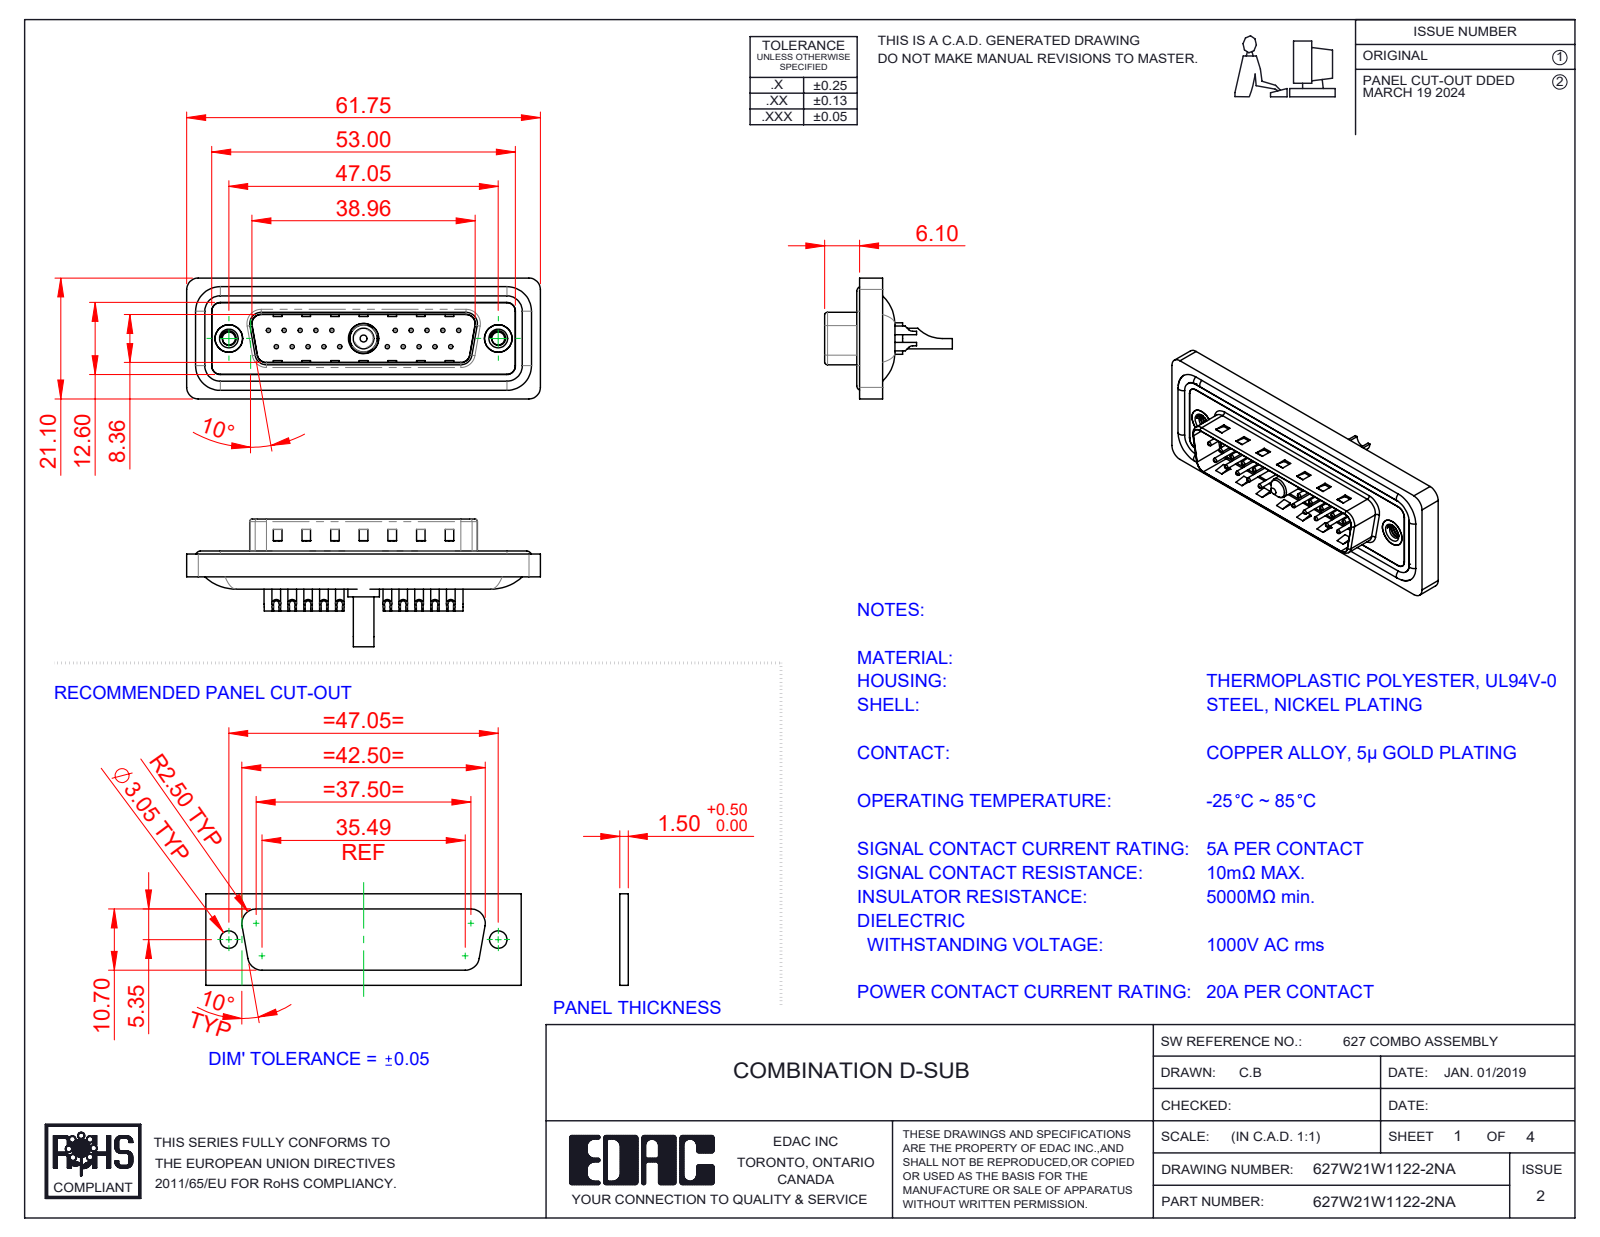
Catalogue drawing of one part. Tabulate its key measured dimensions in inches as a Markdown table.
| quantity | value |
| --- | --- |
| part name | 627Combo Shell Rear_25 Contacts; 627Combo Shell Front_25 Contacts; 627W21W1122-2NA; 627Combo Threaded Rivet_A (+5 more) |
| STEP written by | SolidWorks 2023 (CONFIG_CONTROL_DESIGN) |
| units | inches |
| bodies | 29 solids, 1266 faces (402 planar, 532 cylindrical, 332 other) |
| overall size | 2.431 × 0.878 × 0.831 |
| volume | 0.442 in³ |
| surface area | 18.9 in² |
| round holes (diameter × count) | 0.03 × 20, 0.039 × 20, 0.063 × 20, 0.079 × 20, 0.089 × 2, 0.157 × 2, 0.189 × 2, 0.197 × 2, 0.106 × 1, 0.191 × 1, 0.209 × 1 |
| round bosses / shafts (diameter × count) | 0.059 × 20, 0.063 × 4, 0.193 × 2, 0.217 × 1, 0.205 × 1, 0.187 × 1, 0.148 × 1, 0.142 × 1 |
| partial cylindrical surfaces (radius × count) | 0.059 × 22, 0.079 × 18, 0.02 × 8, 0.063 × 8, 0.039 × 6, 0.01 × 4, 0.024 × 4, 0.026 × 4 |
| main face-to-face distances | 0.016, 0.059, 0.043, 0.063, 0.02, 0.122, 0.114, 0.161, 0.032, 0.377 |
| hole center spacings | 0.124, 0.109, 0.218, 0.327, 0.198, 0.763, 0.826, 0.872 |
